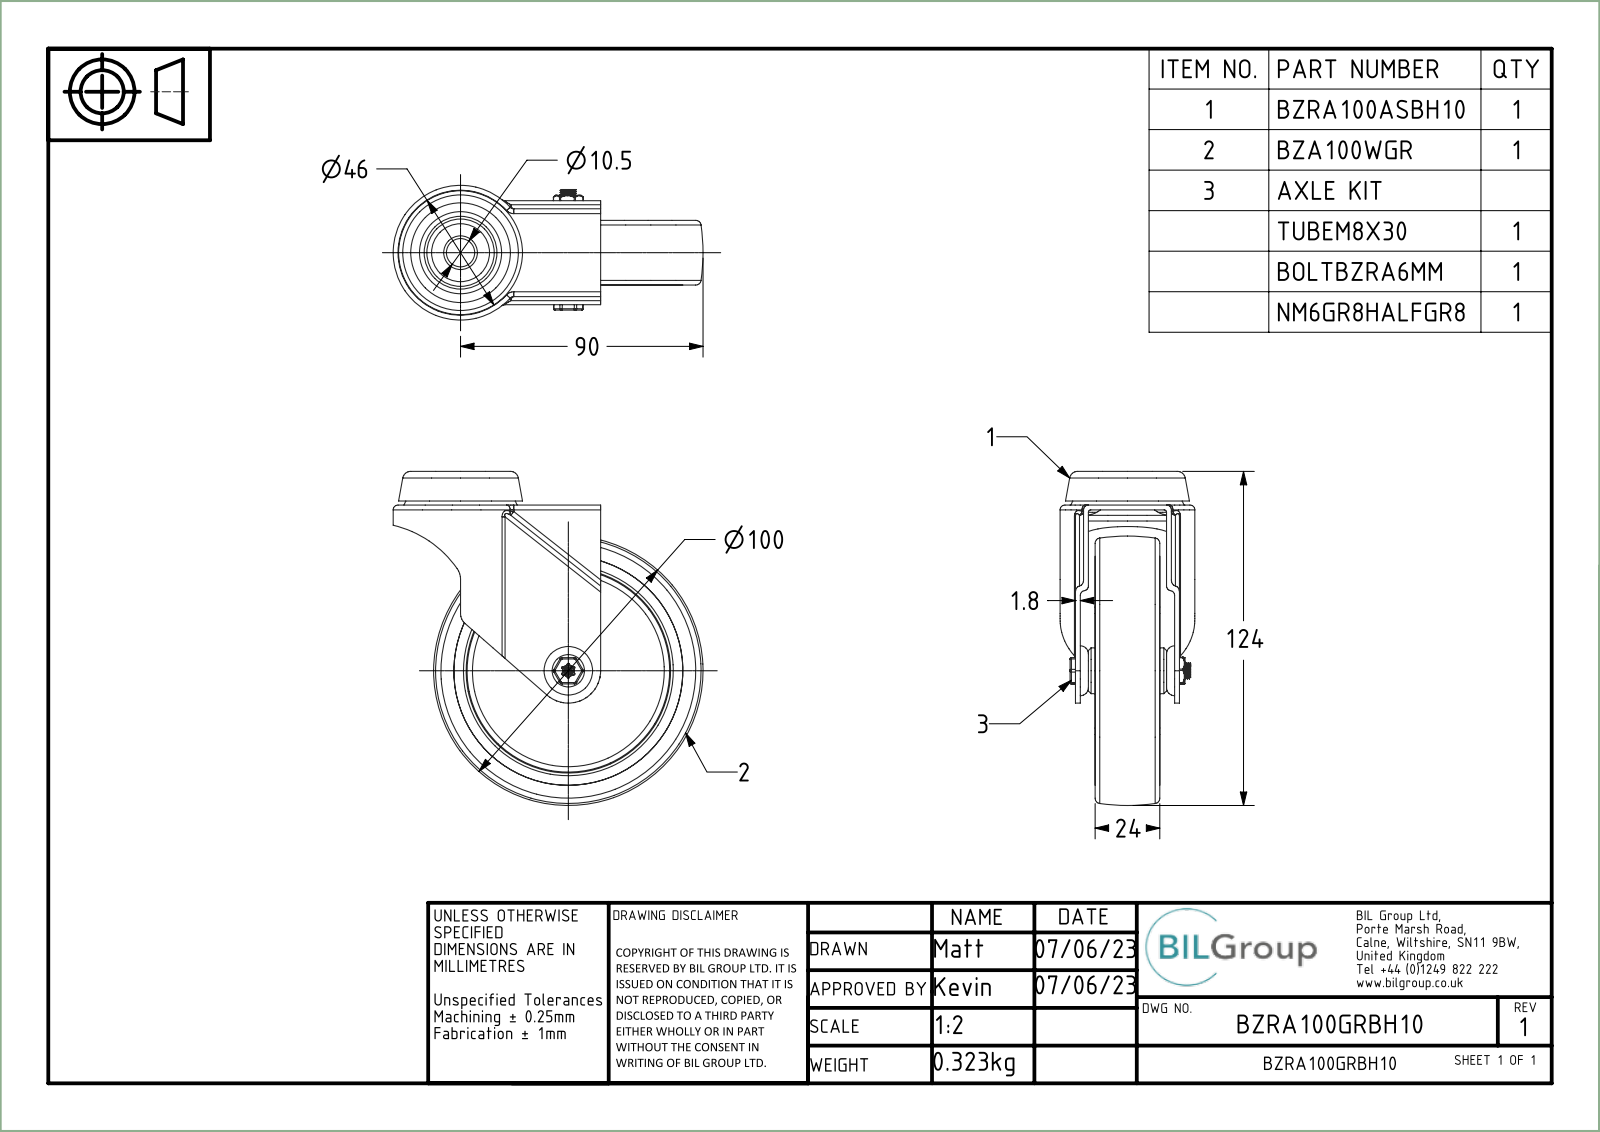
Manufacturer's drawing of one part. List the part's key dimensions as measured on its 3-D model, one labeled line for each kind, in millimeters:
Part name (STEP PRODUCT): BZRA100ASBH10; ZINC PLATED PRESSED STEEL HEAD; ZINC PLATED PRESSED STEEL FORKS; BZRA100GRBH10 (+8 more)
STEP written by: Spatial InterOp 3D (CONFIG_CONTROL_DESIGN)
Units: millimetres
Bodies: 7 solids, 393 faces (60 planar, 169 cylindrical, 164 other)
Overall size (bounding box): 124 × 115 × 50
Volume: 141 370 mm³ · Surface area: 73 196 mm²
Round holes (diameter × count): ⌀6 ×1, ⌀6.3 ×1, ⌀6.4 ×1, ⌀8.3 ×1, ⌀8.4 ×1, ⌀10.5 ×1, ⌀10.56 ×1, ⌀30 ×1, ⌀85 ×1
Round bosses / shafts (diameter × count): ⌀39 ×1, ⌀18 ×1, ⌀17 ×1, ⌀14.76 ×1, ⌀8 ×1, ⌀7.95 ×1, ⌀5 ×1
Partial cylindrical surfaces — rounded edges, fillets, slot ends (radius × count): R1 ×18, R1.8 ×18, R0.5 ×12, R0.4 ×6, R0.9 ×2, R2.12 ×1, R5 ×1, R7 ×1
Main face-to-face distances: 9, 15, 1.8, 6, 33.8, 7.3, 16.3, 22.3, 31.3, 3
